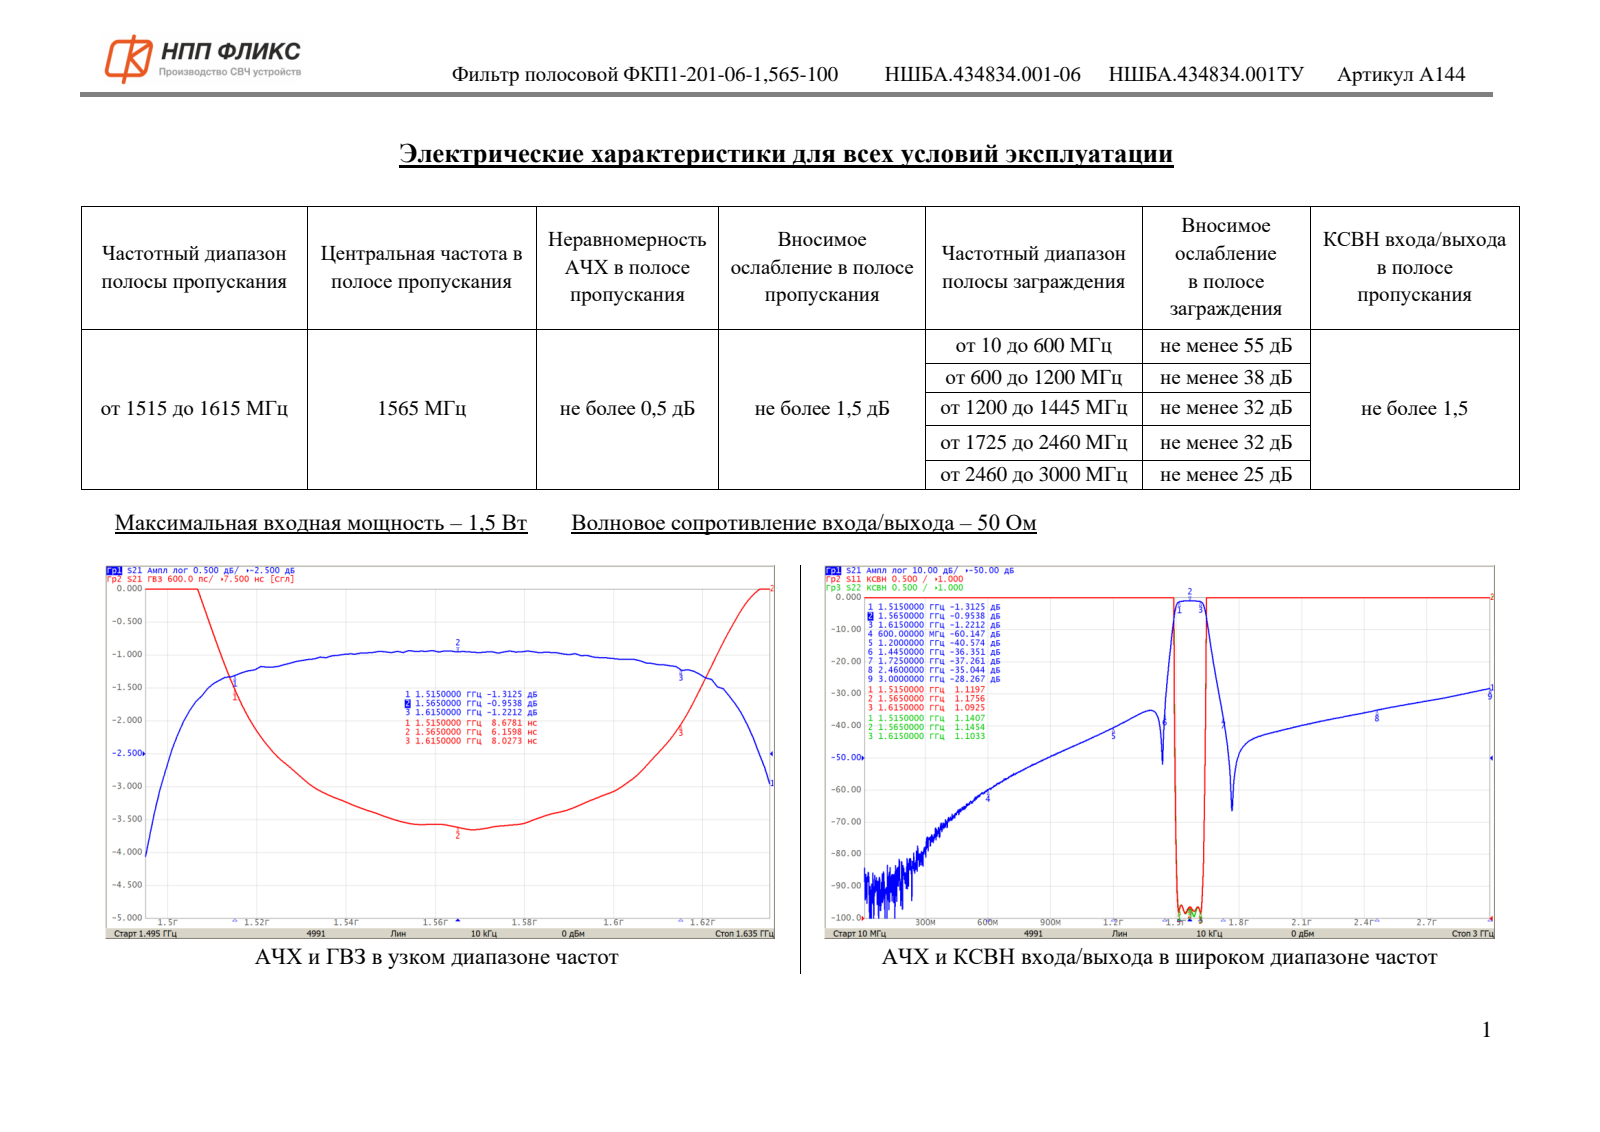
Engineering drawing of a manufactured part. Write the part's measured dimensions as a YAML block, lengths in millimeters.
part_name: "НШБА.434834.001-06_Фильтр ФКП1-201-06-1,565-100"
step_written_by: "ASCON Math Kernel (CONFIG_CONTROL_DESIGN)"
units: millimeters
bodies: {solids: 1, faces: 339, planar: 251, cylindrical: 6, other: 82}
overall_size: [10, 6.15, 4]
volume: 246
surface_area: 252
partial_cylinders:
  - {radius: 0.13, count: 3}
  - {radius: 0.2, count: 1}
  - {radius: 0.23, count: 1}
face_to_face_distances: [4, 6.15, 10, 0.64, 3.36, 2.4, 2.72, 0.9, 0.76, 1.5]
